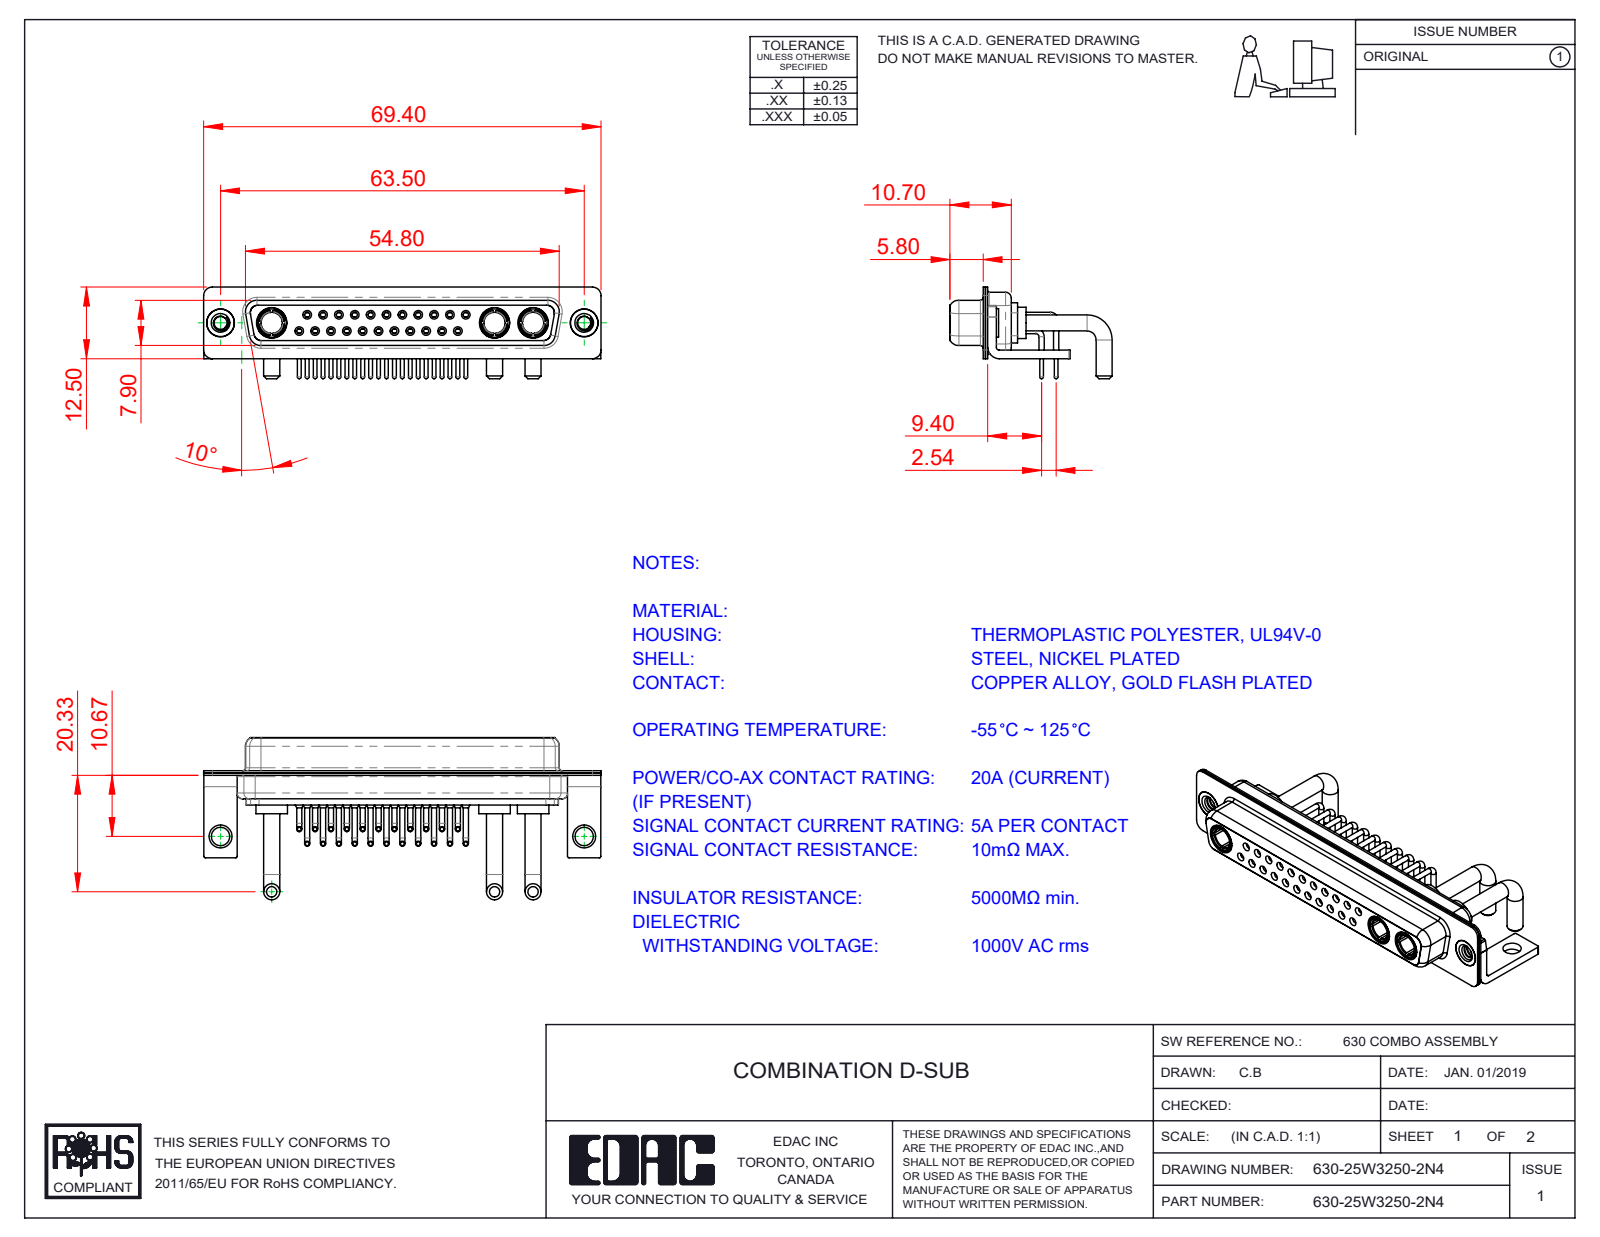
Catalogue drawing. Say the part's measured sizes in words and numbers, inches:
The part is named "Power Socket_Ext 20A RA; 630-25W3250-2N4; 630Combo Shell Front_37 Contacts; 630Combo Contact Row 2 (+5 more)". Its 3-D file was written by "SolidWorks 2020 (CONFIG_CONTROL_DESIGN)". It is 35 solids with 1719 faces: 504 planar, 736 cylindrical and 479 other. Overall it measures 2.732 by 1.115 by 0.63 inches. Its volume is 0.371 cubic inches and its surface area 20.91 square inches. Round holes: 22 of diameter 0.035, 22 of diameter 0.043, 22 of diameter 0.059, 22 of diameter 0.079, 11 of diameter 0.063, 11 of diameter 0.067, 5 of diameter 0.191, 3 of diameter 0.146, 3 of diameter 0.209, 2 of diameter 0.089, 2 of diameter 0.126, 2 of diameter 0.157. Round bosses or shafts: 23 of diameter 0.035, 22 of diameter 0.026, 12 of diameter 0.063, 6 of diameter 0.11, 3 of diameter 0.217, 3 of diameter 0.205, 3 of diameter 0.195, 3 of diameter 0.187. Partial cylindrical surfaces (rounded edges, fillets, slot ends): 16 of radius 0.01, 16 of radius 0.059, 13 of radius 0.079, 8 of radius 0.053, 8 of radius 0.063, 5 of radius 0.02, 4 of radius 0.024, 4 of radius 0.026. The main face-to-face distances are 0.016, 0.018, 0.055, 0.333, 0.071, 0.35, 0.244, 0.278, 0.031, 0.053. The hole center spacings are 0.124, 0.109, 0.218, 0.198, 0.327, 0.294, 0.436, 0.198.
